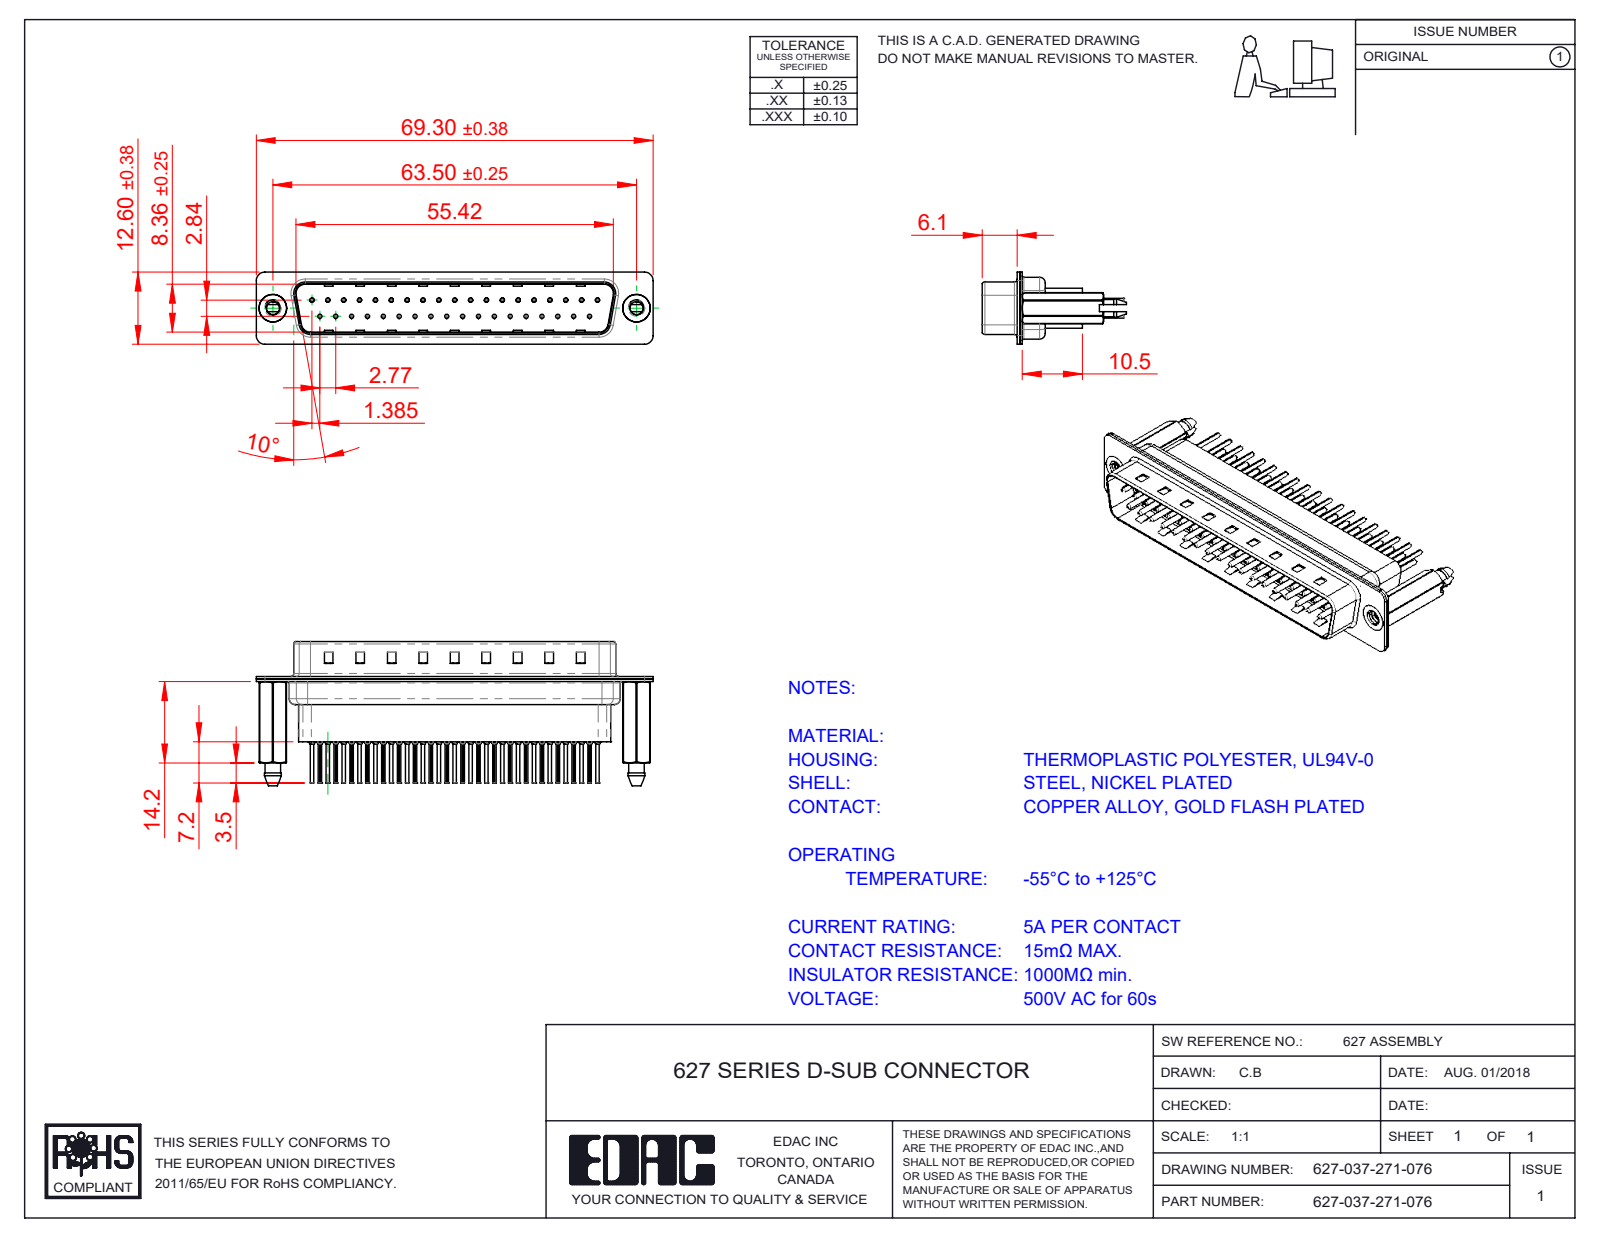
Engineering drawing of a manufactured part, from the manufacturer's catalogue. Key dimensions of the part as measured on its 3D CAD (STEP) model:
Part name (STEP PRODUCT): 627 4-40 Threaded Boardlock_HP71; 627 Shell Rear_37 Contacts; 627 Housing_37 HP; 627 Contact Row 1_61 (+3 more)
STEP written by: SolidWorks 2020 (CONFIG_CONTROL_DESIGN)
Units: millimetres
Bodies: 42 solids, 4146 faces (1123 planar, 1576 cylindrical, 1447 other)
Overall size (bounding box): 69.3 × 25.1 × 12.6
Volume: 5 699 mm³ · Surface area: 14 707 mm²
Round holes (diameter × count): ⌀0.2 ×37, ⌀0.35 ×37, ⌀1.1 ×37, ⌀1.6 ×37, ⌀2.26 ×2, ⌀4 ×2, ⌀4.8 ×2
Round bosses / shafts (diameter × count): ⌀2 ×37, ⌀1.5 ×37, ⌀0.75 ×37, ⌀0.6 ×37, ⌀4.9 ×2
Partial cylindrical surfaces — rounded edges, fillets, slot ends (radius × count): R0.1 ×74, R1.5 ×18, R2 ×12, R1.6 ×10, R0.5 ×8, R0.25 ×4, R0.6 ×4, R0.65 ×4
Main face-to-face distances: 0.4, 0.82, 9.58, 0.68, 7.68, 0.45, 1.5, 1.08, 8.08, 8.76
Hole centre spacings: 3.16, 2.77, 5.54, 8.31, 5.04, 10.1, 11.08, 12.78
